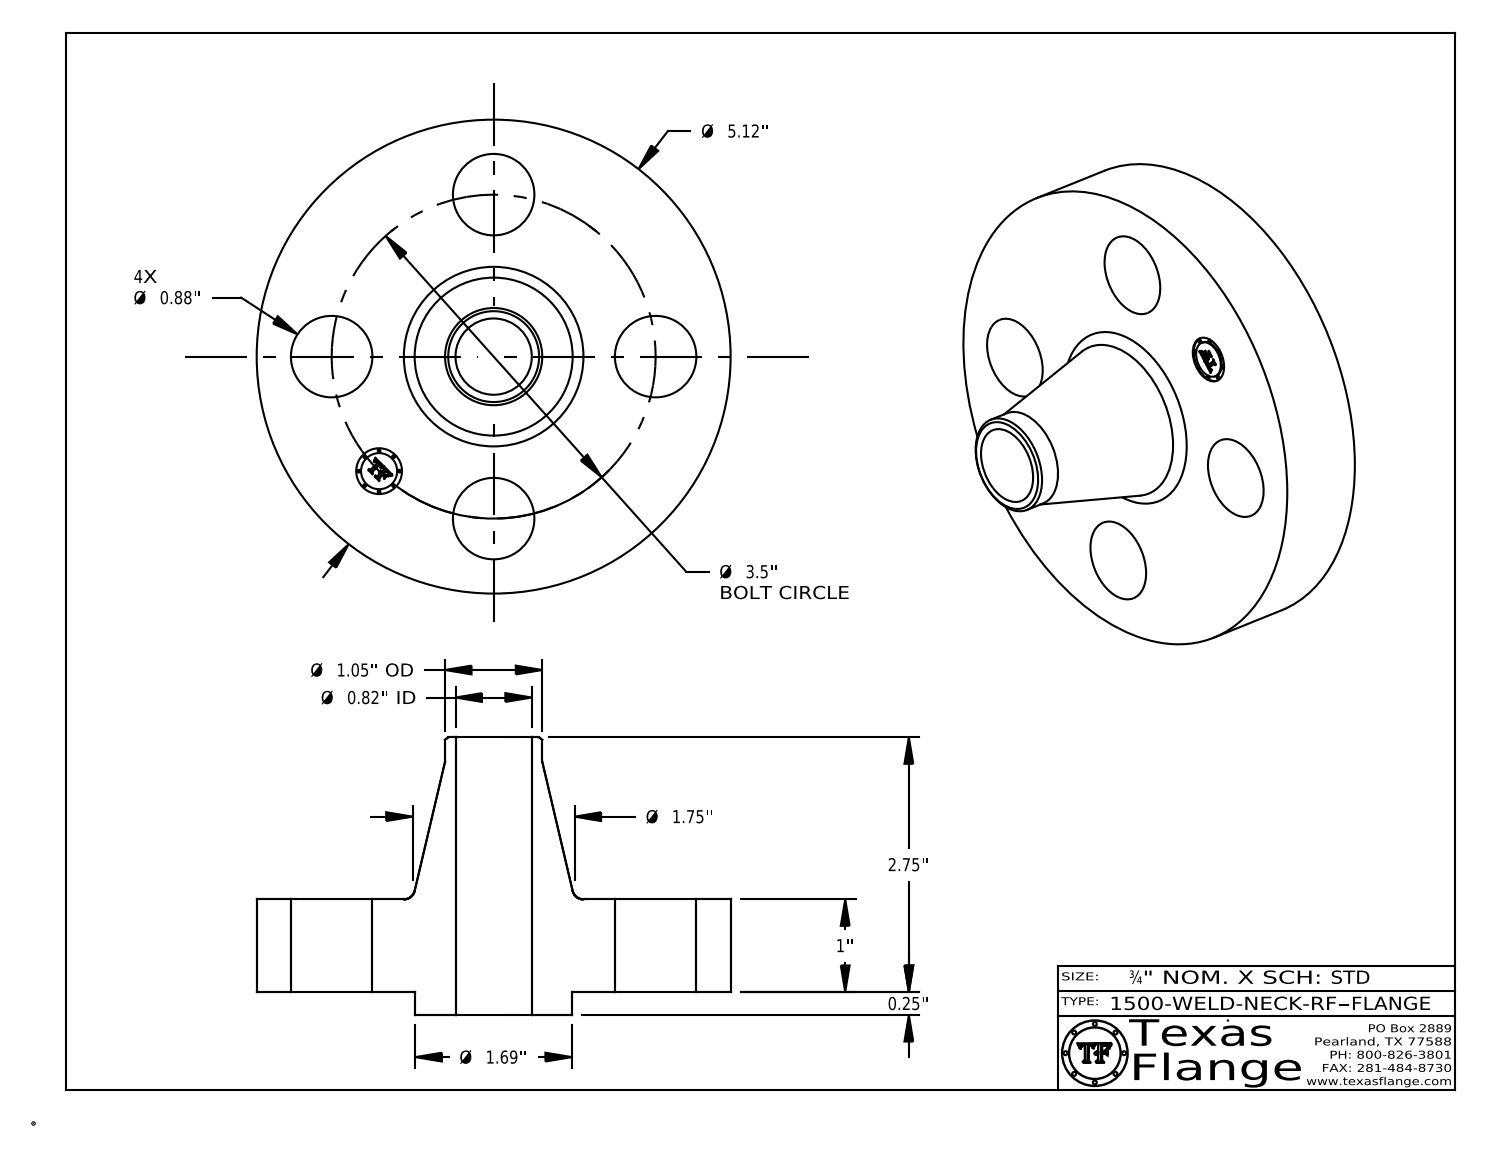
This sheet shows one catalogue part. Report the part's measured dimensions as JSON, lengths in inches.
{"part_name": "1500-WELD-NECK-RF", "step_written_by": "CATIA V5 STEP AP214 (AUTOMOTIVE_DESIGN)", "units": "inches", "bodies": {"solids": 1, "faces": 411, "planar": 369, "cylindrical": 36, "other": 6}, "overall_size": [5.12, 5.12, 3], "volume_in3": 19.69, "surface_area_in2": 77.41, "round_holes": [[0.88, 4], [0.495, 1], [0.824, 1]], "round_bosses_or_shafts": [[0.03, 8], [5.12, 1], [1.69, 1], [1.05, 1], [0.39, 1]], "face_to_face_distances": [1, 0.25, 1.25, 3, 2.75, 1.75, 0.015, 1.235, 0.985, 1.765], "hole_center_spacings": [1.75, 2.475, 1.339, 3.233, 3.5]}
